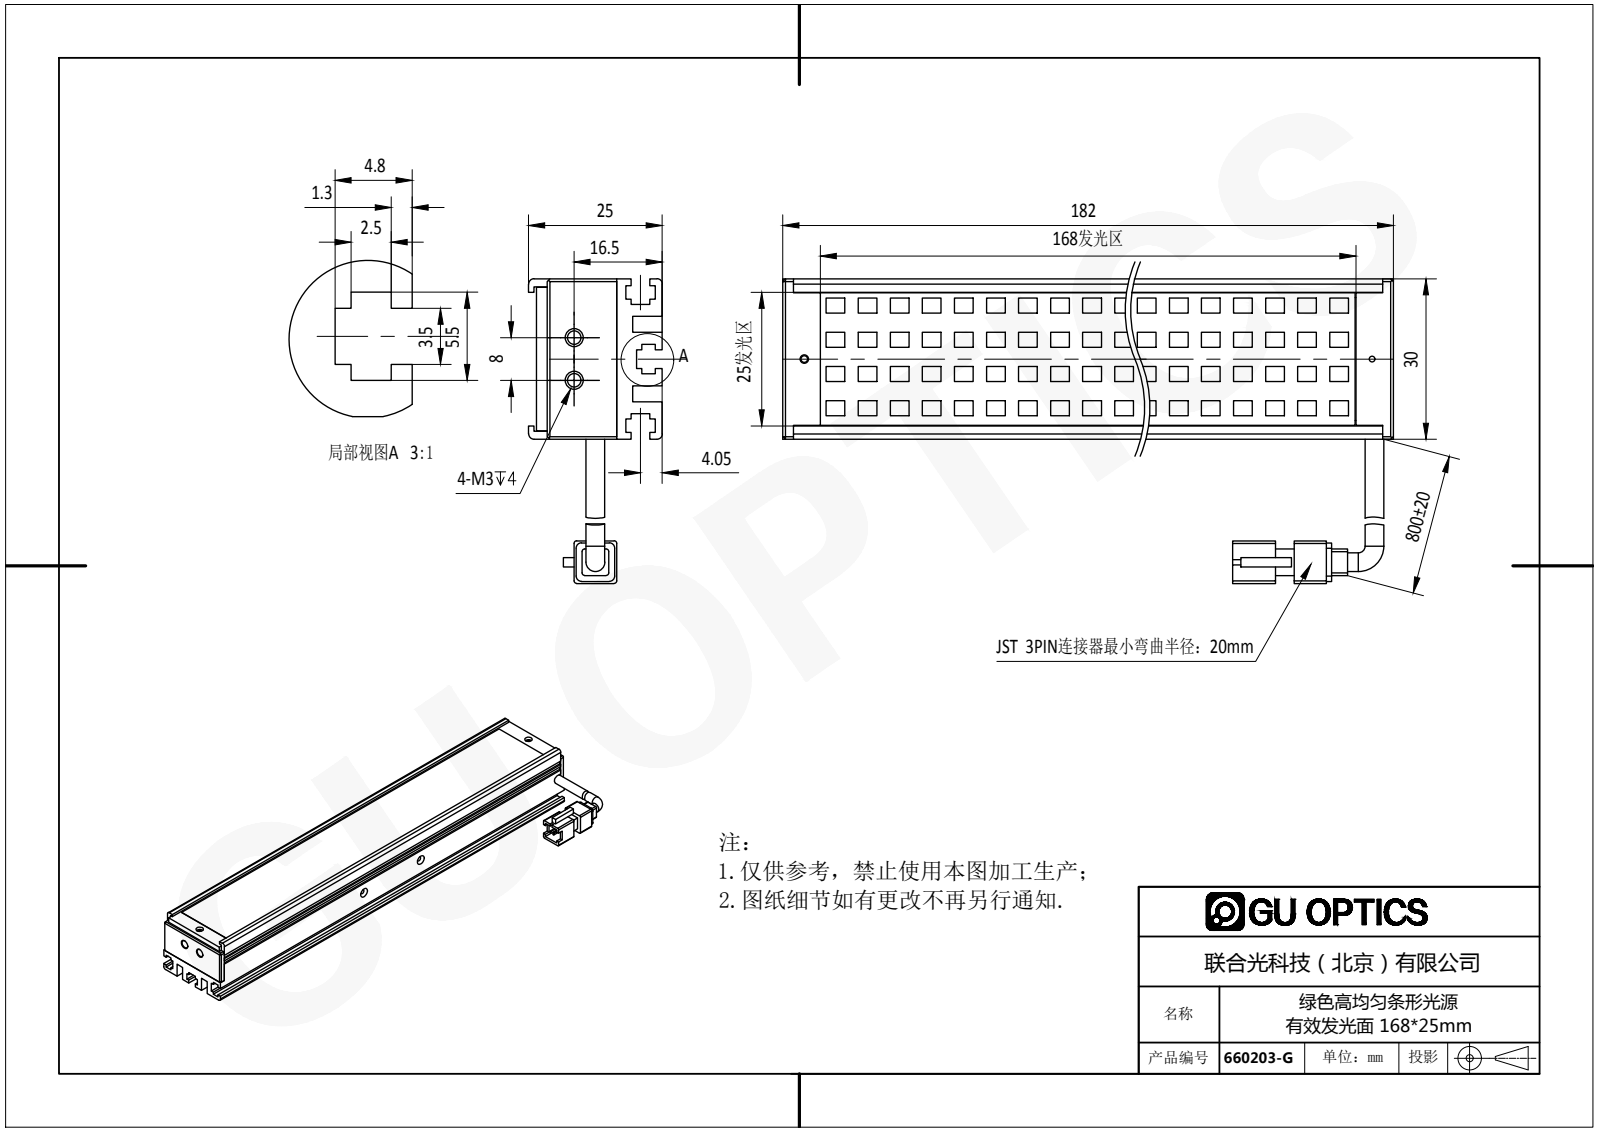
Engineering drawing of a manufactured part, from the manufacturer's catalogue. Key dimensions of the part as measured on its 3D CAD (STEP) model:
Part name (STEP PRODUCT): 660203-G
STEP written by: SolidWorks 2016 (AUTOMOTIVE_DESIGN)
Units: millimetres
Bodies: 6 solids, 1004 faces (818 planar, 83 cylindrical, 103 other)
Overall size (bounding box): 182 × 57 × 25
Volume: 63 499 mm³ · Surface area: 64 448 mm²
Round holes (diameter × count): ⌀1.6 ×5, ⌀1.5 ×2, ⌀1.7 ×2, ⌀2.5 ×2, ⌀2.8 ×2, ⌀3 ×2, ⌀1.1 ×1, ⌀1.25 ×1, ⌀2 ×1
Round bosses / shafts (diameter × count): ⌀3.5 ×2
Partial cylindrical surfaces — rounded edges, fillets, slot ends (radius × count): R1 ×12, R0.5 ×8, R1.65 ×1
Main face-to-face distances: 1, 13, 2, 2.5, 3, 9.5, 27.5, 4.5, 12, 8.5
Hole centre spacings: 174, 7, 72, 72.3, 102, 102.21, 174.14, 8
